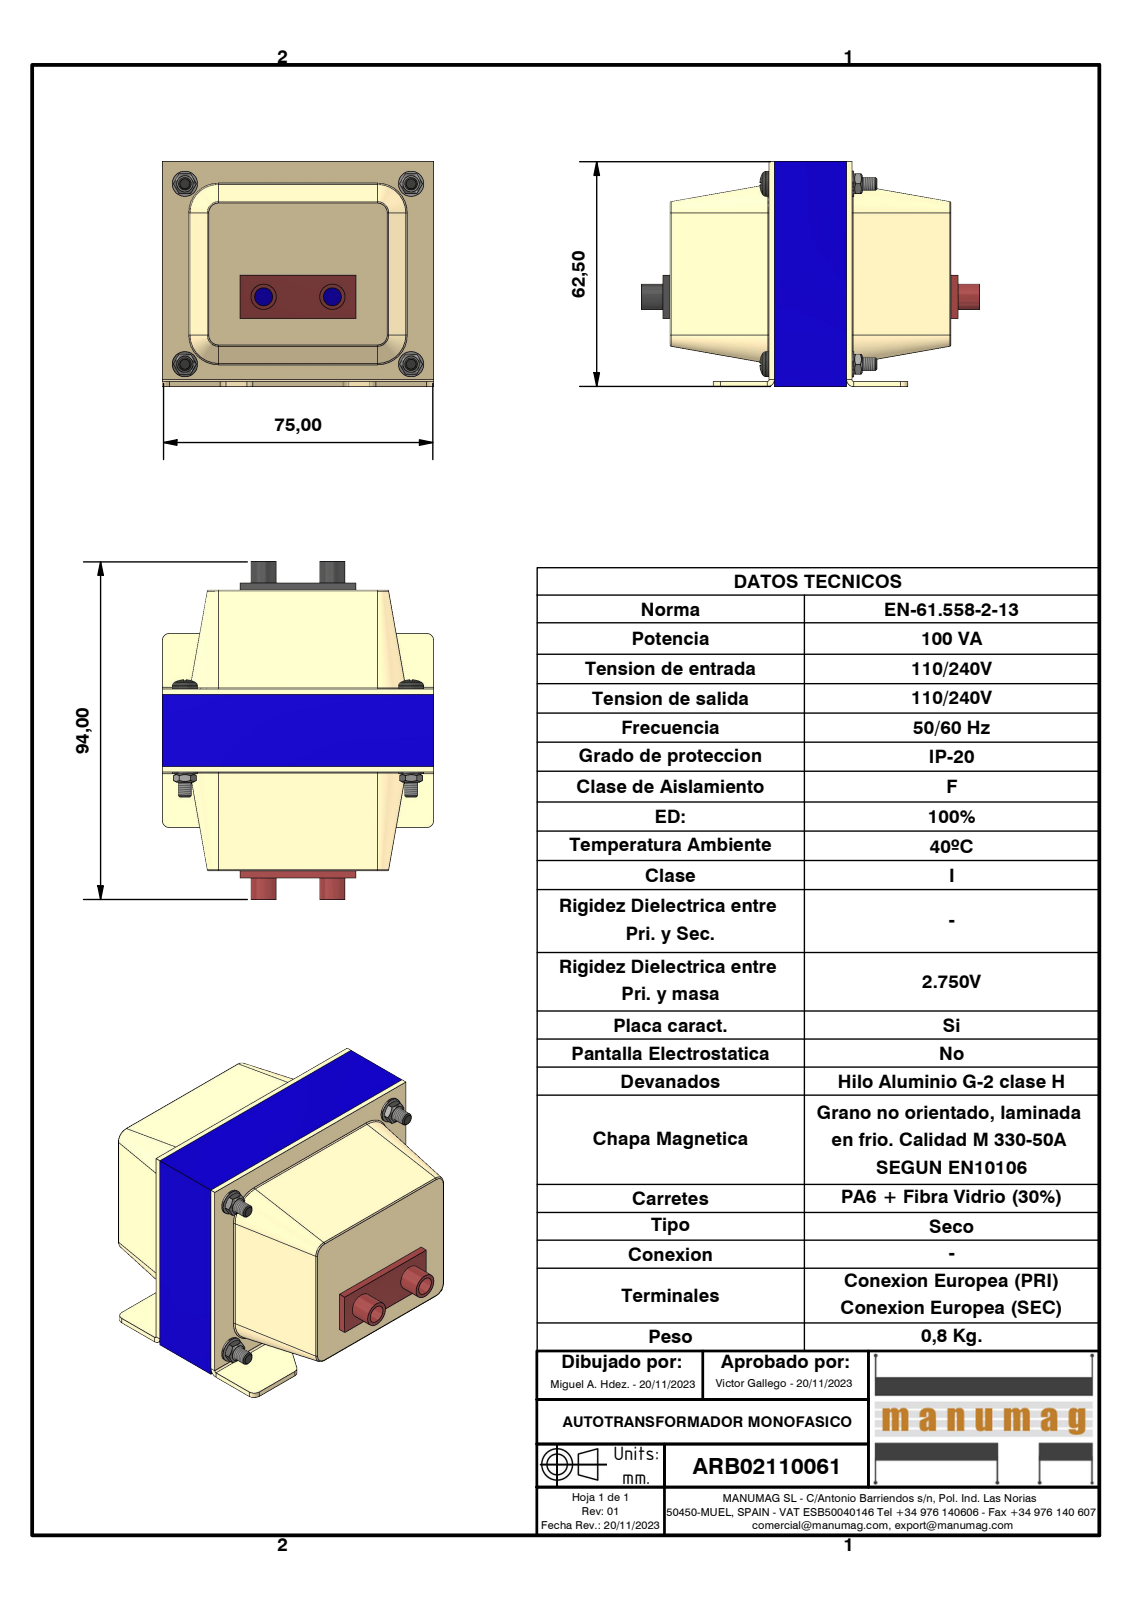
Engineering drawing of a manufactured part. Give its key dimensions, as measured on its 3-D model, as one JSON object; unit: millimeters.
{"part_name": "ARB02110061; TAPA RC25 RECEPTACULO; Receptaculo negro; Receptaculo Rojo (+4 more)", "step_written_by": "Autodesk Inventor 2023 (AUTOMOTIVE_DESIGN)", "units": "millimeters", "bodies": {"solids": 17, "faces": 366, "planar": 170, "cylindrical": 72, "other": 124}, "overall_size": [94, 75, 62.5], "volume_mm3": 92410, "surface_area_mm2": 62250, "round_holes": [[2.46, 4], [3, 4], [3.2, 4], [4.5, 4], [5, 2]], "round_bosses_or_shafts": [[7, 6], [3.5, 4], [3.18, 4]], "partial_cylinders_radius": [[0.38, 16], [2, 14], [0.5, 2]], "face_to_face_distances": [1.5, 49, 27.5, 20, 12.5, 29, 62.56, 52.71, 21.5, 50.5], "hole_center_spacings": [28.67, 38.13, 44.83, 50, 51.4, 62.5, 80.04, 19]}
